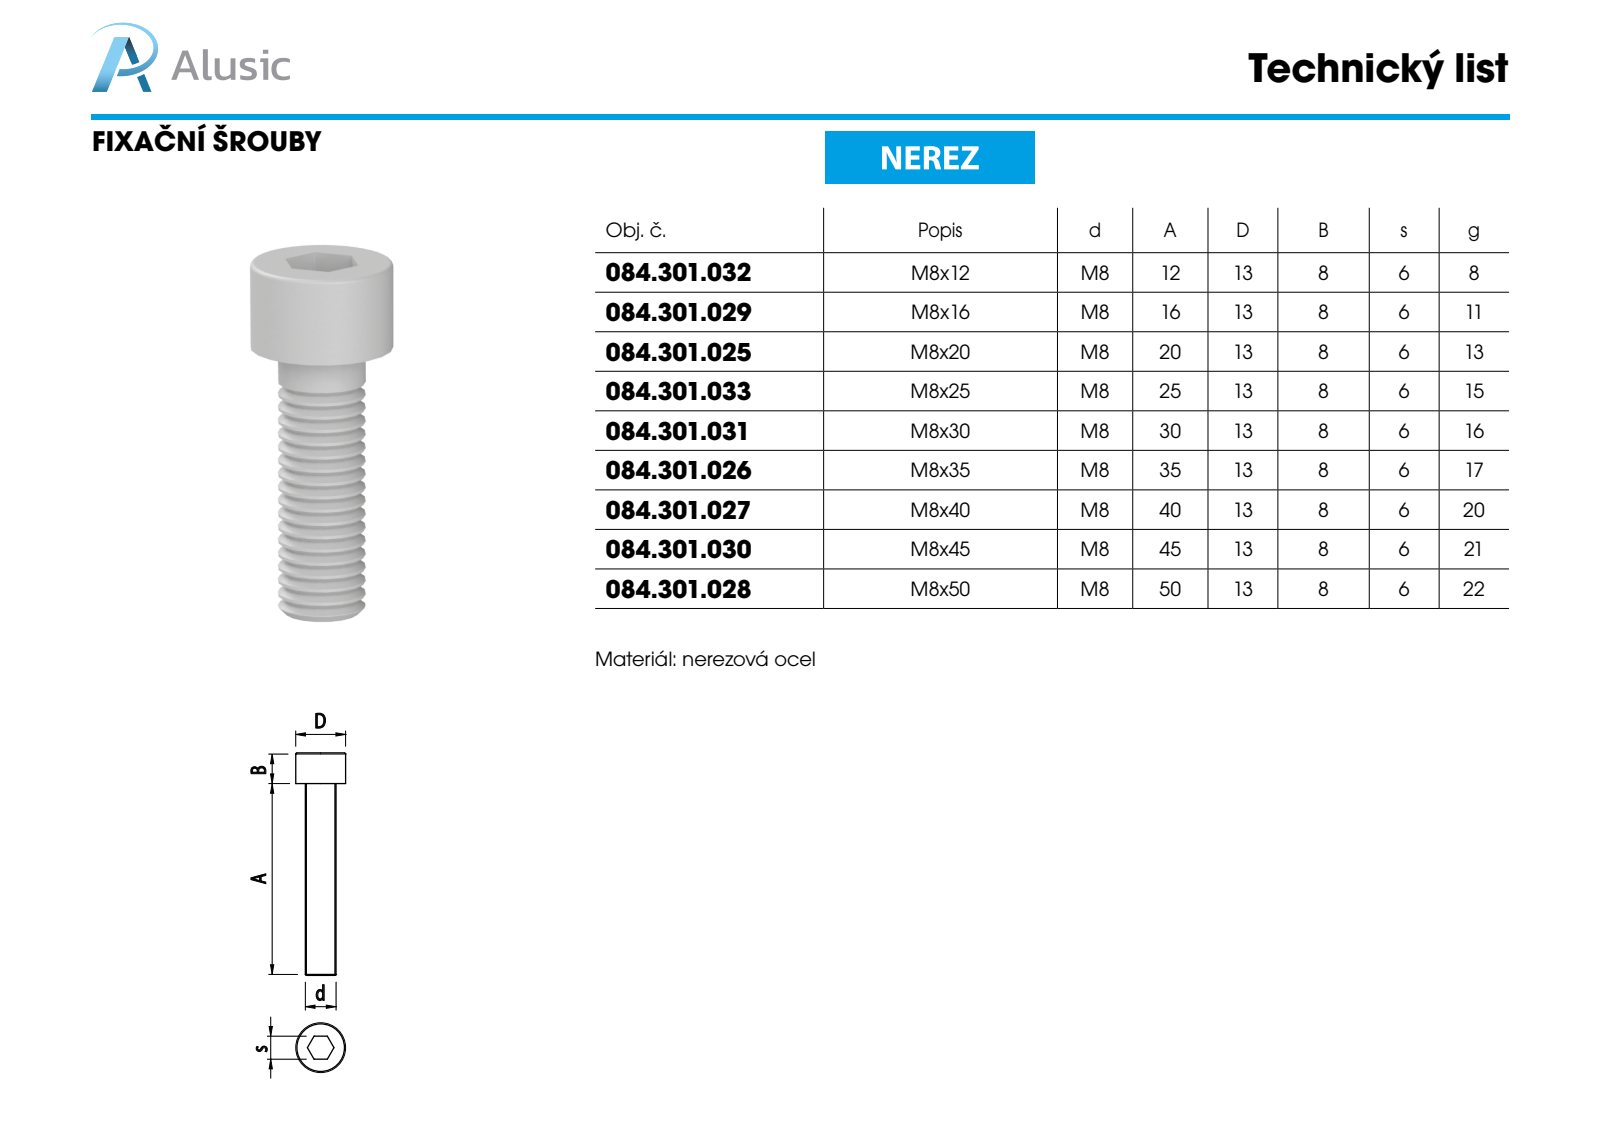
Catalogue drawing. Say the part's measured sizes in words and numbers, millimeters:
The part is named "084.301.033". Its 3-D file was written by "SolidWorks 2016 (CONFIG_CONTROL_DESIGN)". It is 1 solid with 56 faces: 12 planar, 39 cylindrical and 5 other. Overall it measures 33 by 13 by 13 millimeters. Its volume is 1 959 cubic millimeters and its surface area 1 578 square millimeters. Round bosses or shafts: 1 of diameter 13, 1 of diameter 8. The main face-to-face distances are 8, 6, 25, 33, 28, 3, 5.
